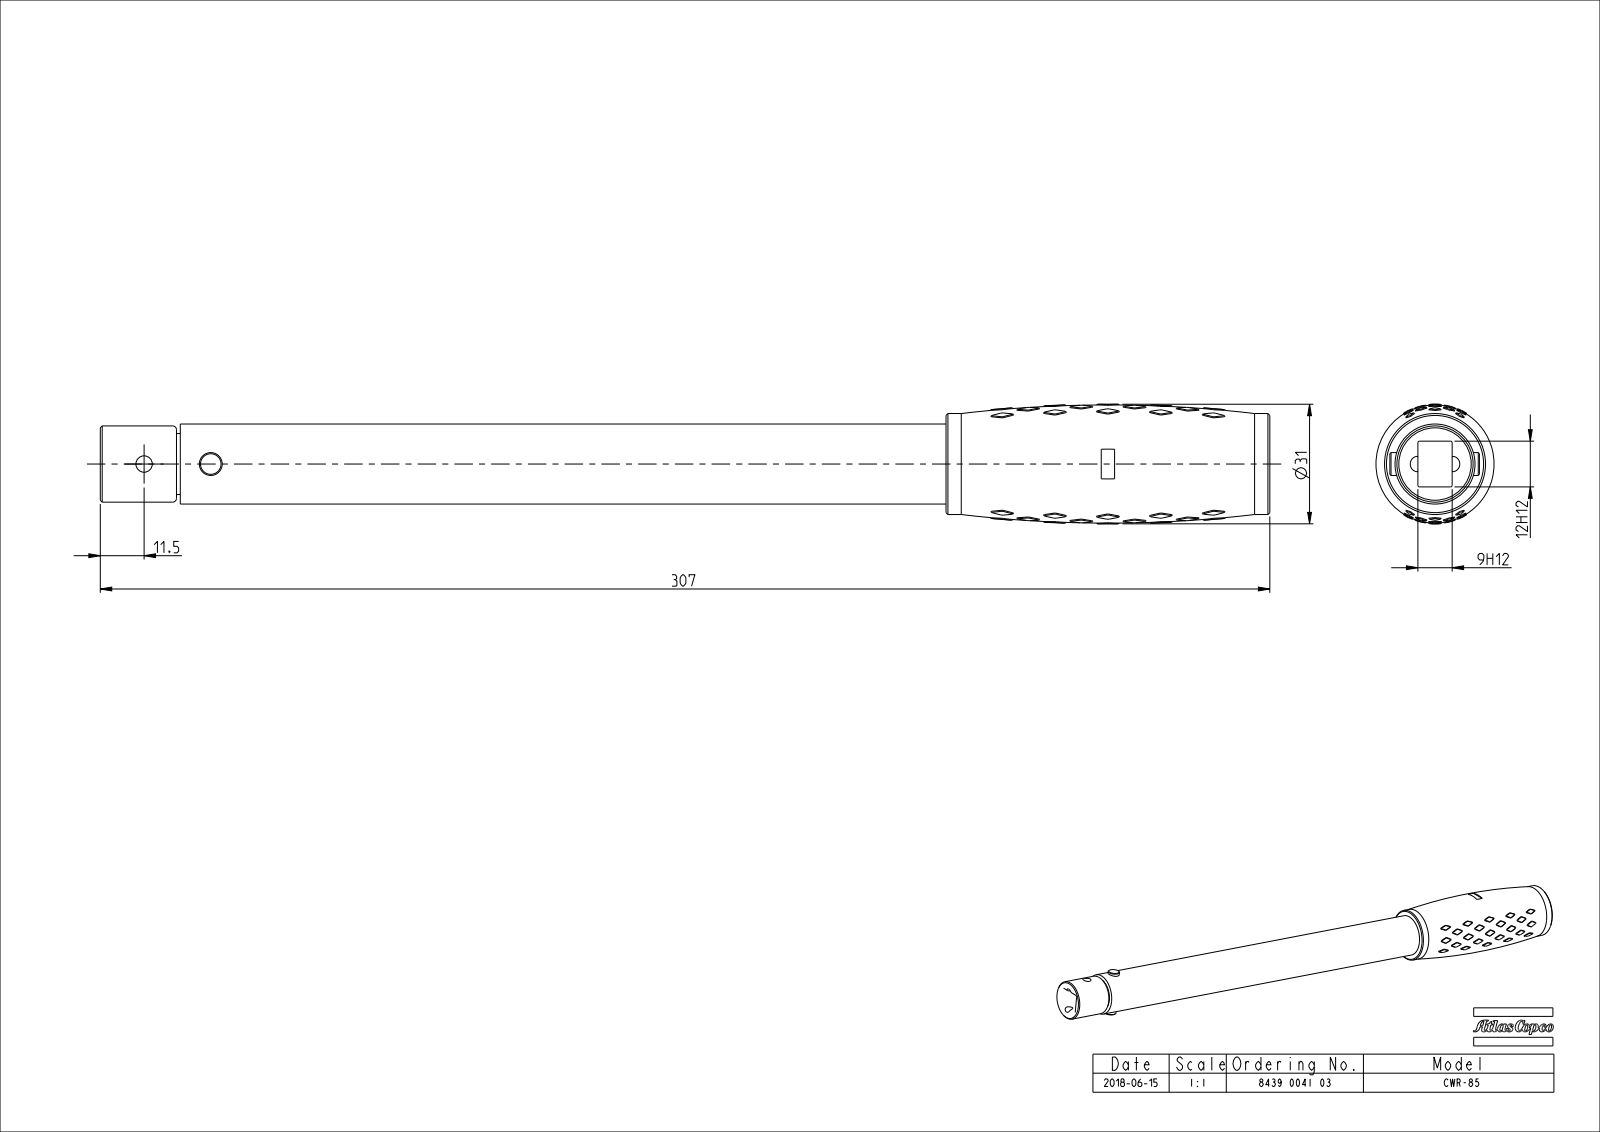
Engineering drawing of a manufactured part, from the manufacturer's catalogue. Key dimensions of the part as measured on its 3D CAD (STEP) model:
Part name (STEP PRODUCT): 8439004103_SW0001
STEP written by: CREO PARAMETRIC BY PTC INC, 2018100 (CONFIG_CONTROL_DESIGN)
Units: millimetres
Bodies: 2 solids, 635 faces (80 planar, 92 cylindrical, 463 other)
Overall size (bounding box): 307 × 31.41 × 31
Volume: 60 648 mm³ · Surface area: 40 800 mm²
Round holes (diameter × count): ⌀4.3 ×1, ⌀9 ×1, ⌀10.5 ×1, ⌀17 ×1, ⌀18 ×1
Round bosses / shafts (diameter × count): ⌀26.5 ×1, ⌀21 ×1, ⌀20 ×1, ⌀6 ×1
Partial cylindrical surfaces — rounded edges, fillets, slot ends (radius × count): R0.4 ×4, R2 ×4, R2.5 ×2, R4.2 ×1
Main face-to-face distances: 288, 2, 265, 23, 9, 203, 62, 85, 12, 205
